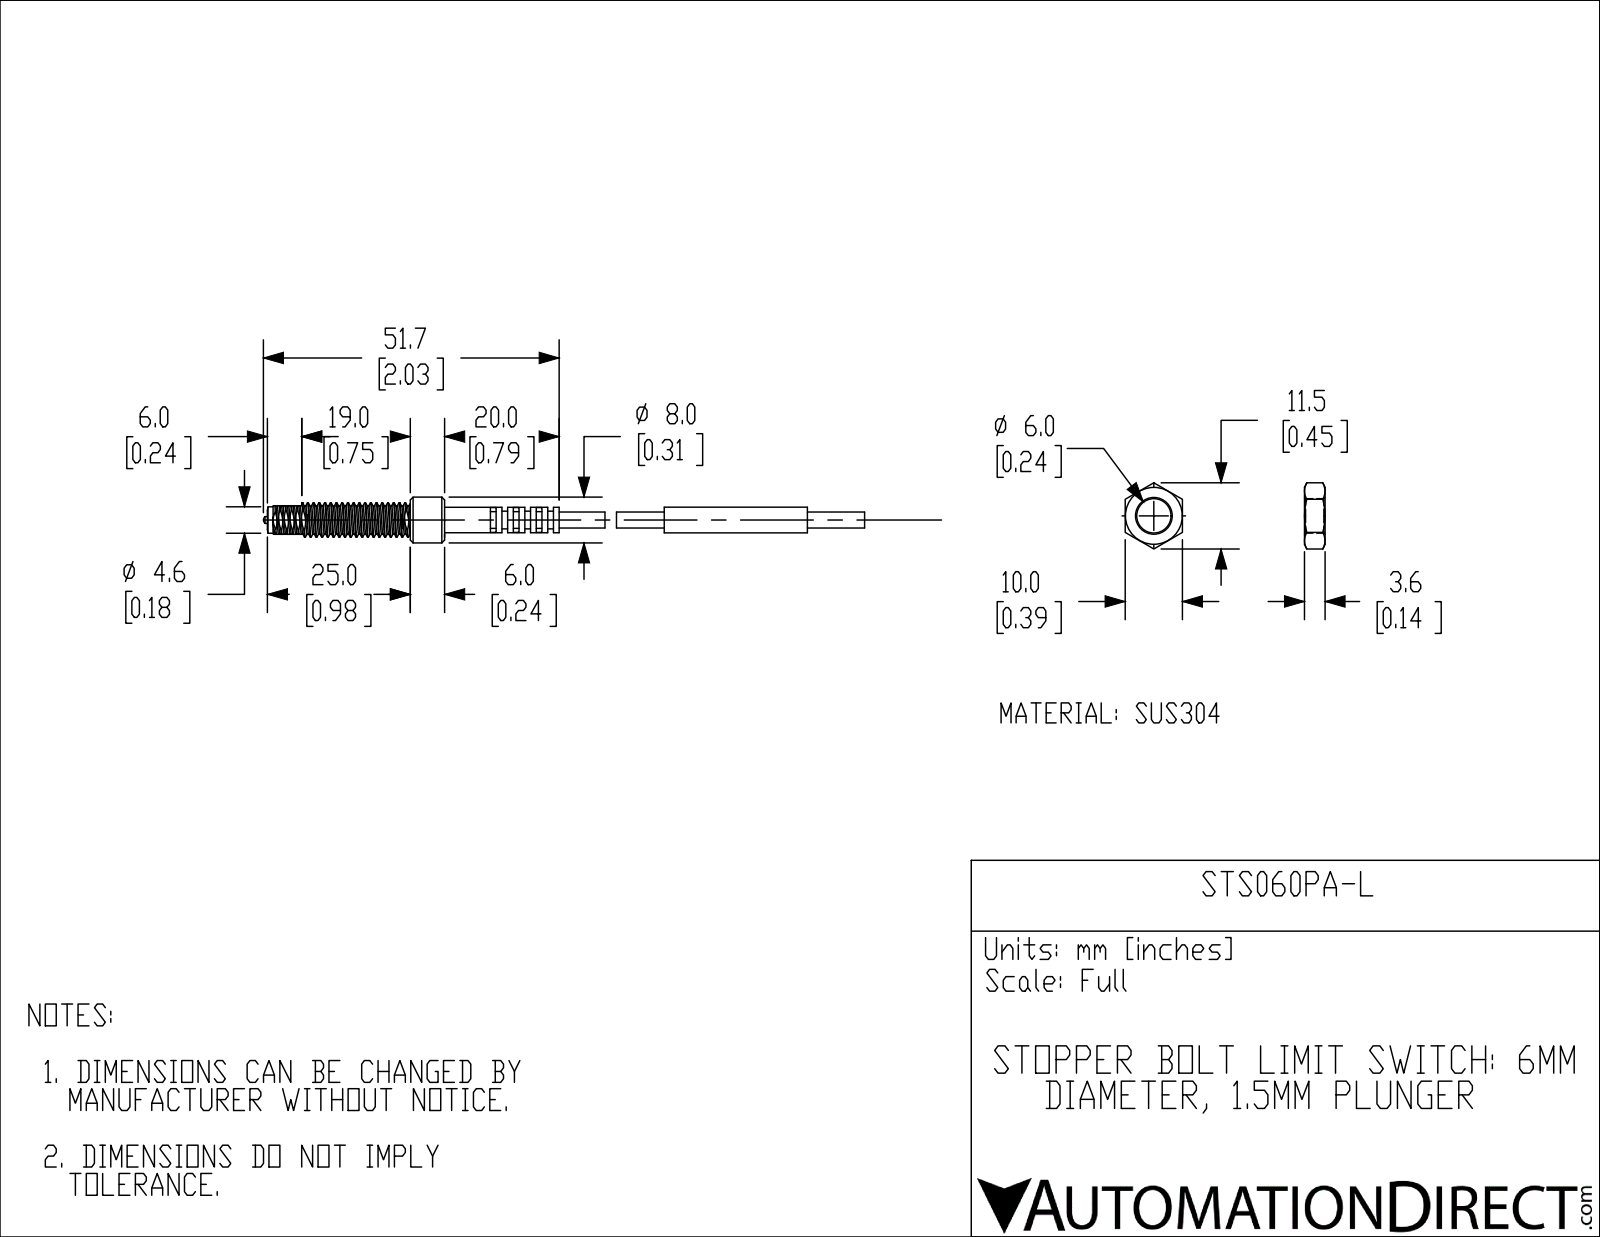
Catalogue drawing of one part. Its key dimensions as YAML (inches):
part_name: "STS060PA-L"
step_written_by: "SolidWorks 2018 (AUTOMOTIVE_DESIGN)"
units: inches
bodies: {solids: 2, faces: 82, planar: 50, cylindrical: 22, other: 10}
overall_size: [4.134, 0.315, 0.315]
volume: 0.109
surface_area: 2.579
round_bosses_or_shafts:
  - {diameter: 0.315, count: 1}
  - {diameter: 0.236, count: 1}
  - {diameter: 0.181, count: 1}
  - {diameter: 0.177, count: 1}
  - {diameter: 0.175, count: 1}
  - {diameter: 0.122, count: 1}
  - {diameter: 0.11, count: 1}
  - {diameter: 0.047, count: 1}
face_to_face_distances: [0.197, 0.039, 0.079, 0.118, 0.157, 0.236, 0.315, 0.354, 0.394, 0.276]
